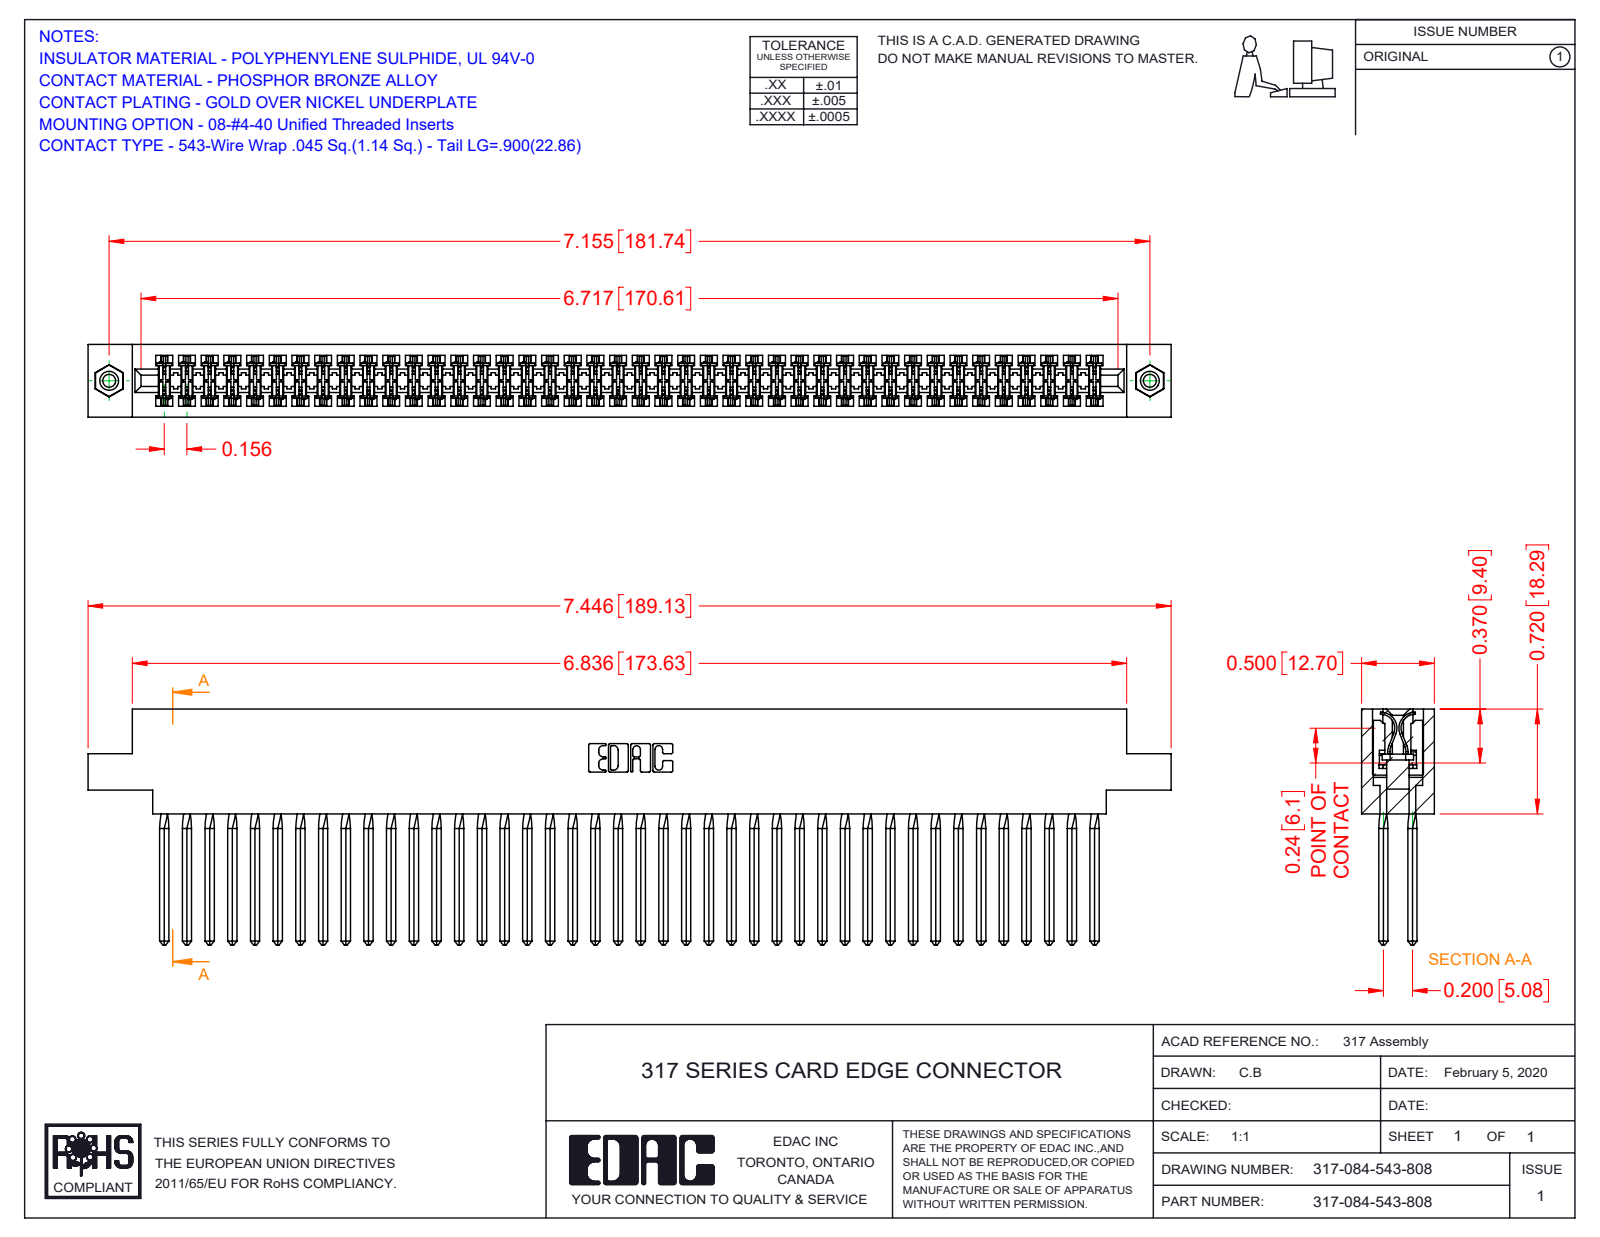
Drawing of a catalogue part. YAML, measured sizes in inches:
part_name: "345-250-001_345-250-003-102; 317-290-001_543; 317 Part_.156 Dia - TI; 317-084-543-808"
step_written_by: "SolidWorks 2016 (CONFIG_CONTROL_DESIGN)"
units: inches
bodies: {solids: 87, faces: 7638, planar: 6222, cylindrical: 1064, other: 352}
overall_size: [7.446, 1.62, 0.5]
volume: 1.962
surface_area: 75.64
round_holes:
  - {diameter: 0.089, count: 2}
  - {diameter: 0.125, count: 2}
  - {diameter: 0.156, count: 2}
round_bosses_or_shafts:
  - {diameter: 0.155, count: 2}
partial_cylinders:
  - {radius: 0.015, count: 168}
  - {radius: 0.01, count: 22}
  - {radius: 0.007, count: 6}
  - {radius: 0.031, count: 6}
  - {radius: 0.026, count: 3}
  - {radius: 0.095, count: 2}
  - {radius: 0.1, count: 2}
  - {radius: 0.11, count: 2}
face_to_face_distances: [0.5, 0.075, 0.425, 0.35, 0.195, 0.11, 0.094, 0.2, 0.115, 0.131]
hole_center_spacings: [7.155]
